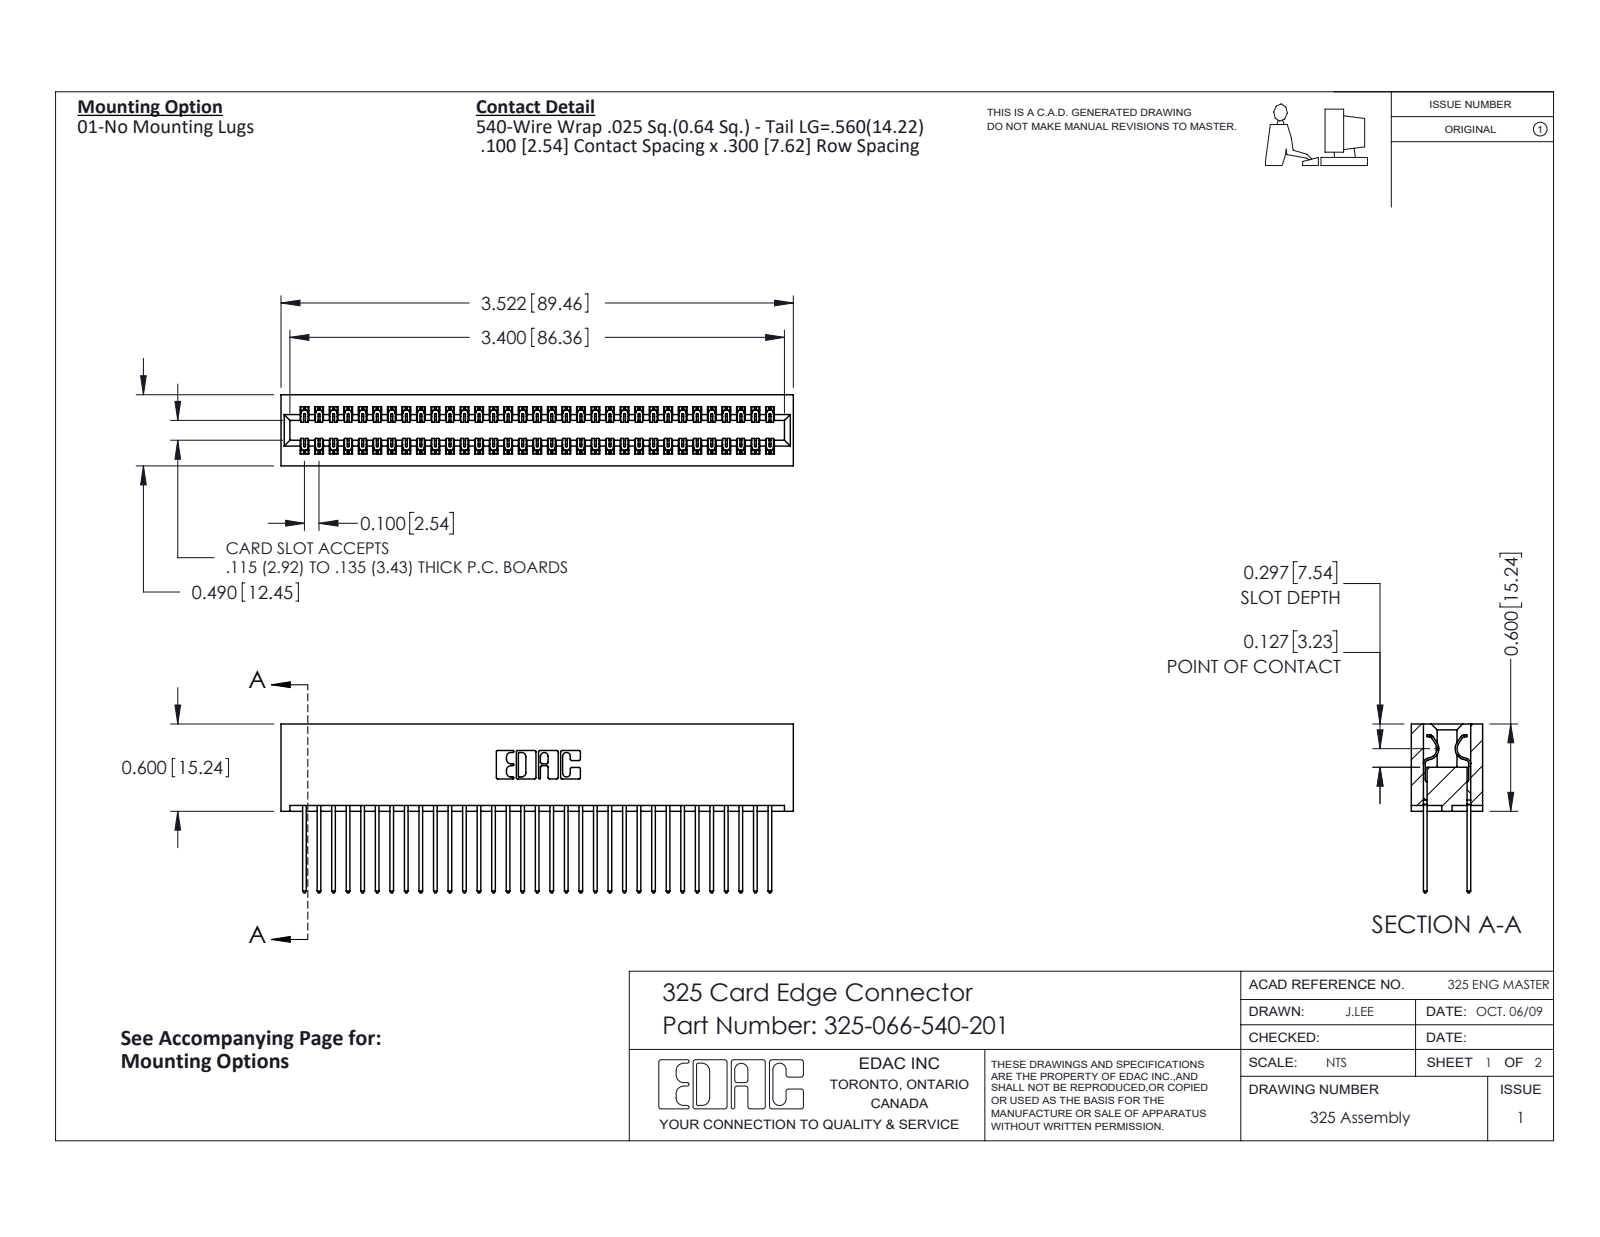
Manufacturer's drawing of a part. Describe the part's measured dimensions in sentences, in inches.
The part is named "325 Part_Lugless; 325-292-001_325-293-140; 325-066-540-201". Its 3-D file was written by "SolidWorks 2016 (CONFIG_CONTROL_DESIGN)". It is 67 solids with 3538 faces: 2442 planar, 1096 cylindrical and 0 other. Overall it measures 3.522 by 1.16 by 0.49 inches. Its volume is 0.752 cubic inches and its surface area 25.66 square inches. Partial cylindrical surfaces (rounded edges, fillets, slot ends): 99 of radius 0.006, 66 of radius 0.01, 22 of radius 0.01, 6 of radius 0.007, 6 of radius 0.031, 3 of radius 0.026, 2 of radius 0.014, 2 of radius 0.022. The main face-to-face distances are 0.083, 0.407, 0.3, 0.107, 0.383, 0.025, 0.325, 0.49, 0.275, 0.56.
